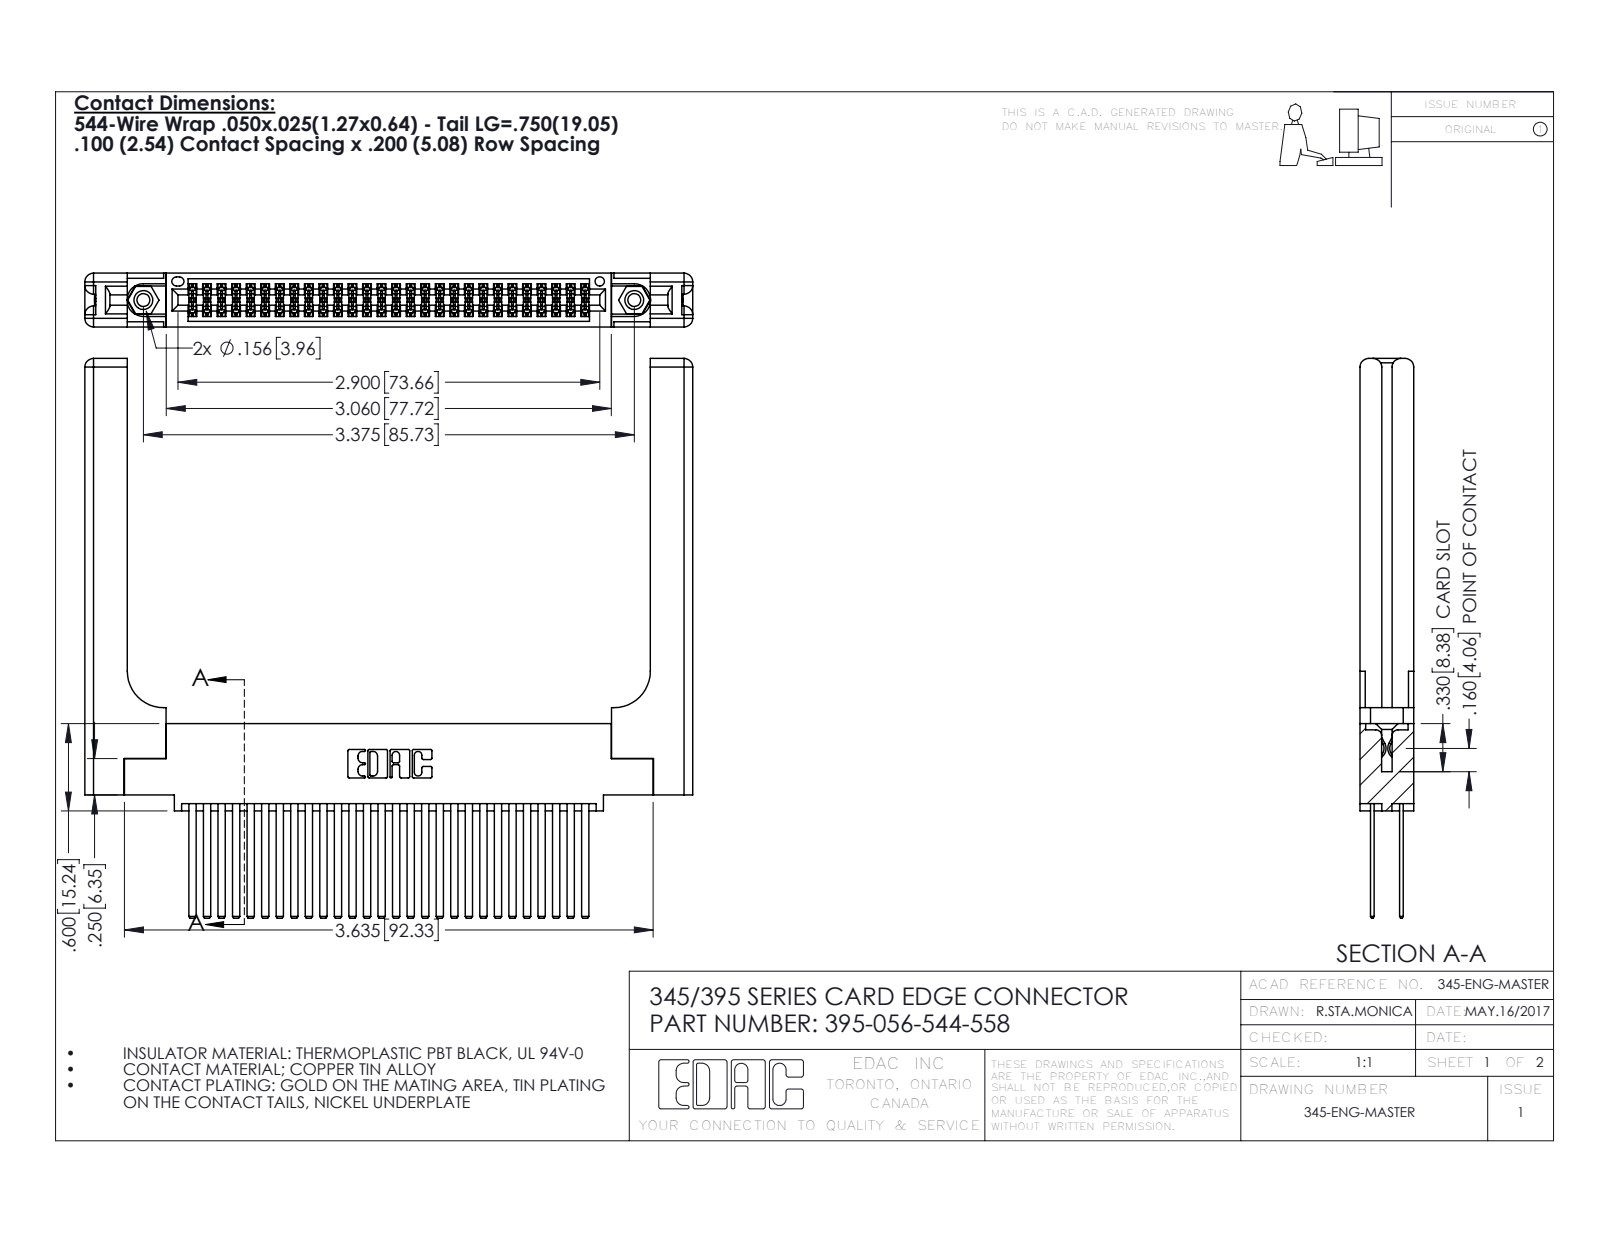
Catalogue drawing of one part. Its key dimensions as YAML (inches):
part_name: "345-220-058_345-220-058; 345-292-001_345-293-144; 345-250-001_345-250-001-102; 345 Part_0.110 Offset - 0.156 Dia-TH (+1 more)"
step_written_by: "SolidWorks 2016 (CONFIG_CONTROL_DESIGN)"
units: inches
bodies: {solids: 61, faces: 2850, planar: 1856, cylindrical: 934, other: 60}
overall_size: [4.179, 3.847, 0.37]
volume: 1.182
surface_area: 36.09
round_holes:
  - {diameter: 0.089, count: 2}
  - {diameter: 0.125, count: 2}
  - {diameter: 0.156, count: 2}
  - {diameter: 0.064, count: 1}
round_bosses_or_shafts:
  - {diameter: 0.155, count: 2}
partial_cylinders:
  - {radius: 0.006, count: 84}
  - {radius: 0.01, count: 22}
  - {radius: 0.06, count: 16}
  - {radius: 0.007, count: 6}
  - {radius: 0.031, count: 6}
  - {radius: 0.026, count: 3}
  - {radius: 0.014, count: 2}
  - {radius: 0.019, count: 2}
face_to_face_distances: [0.072, 0.298, 0.098, 0.272, 0.025, 0.2, 0.37, 0.225, 0.175, 0.148]
hole_center_spacings: [0.27, 3.14, 3.375]
